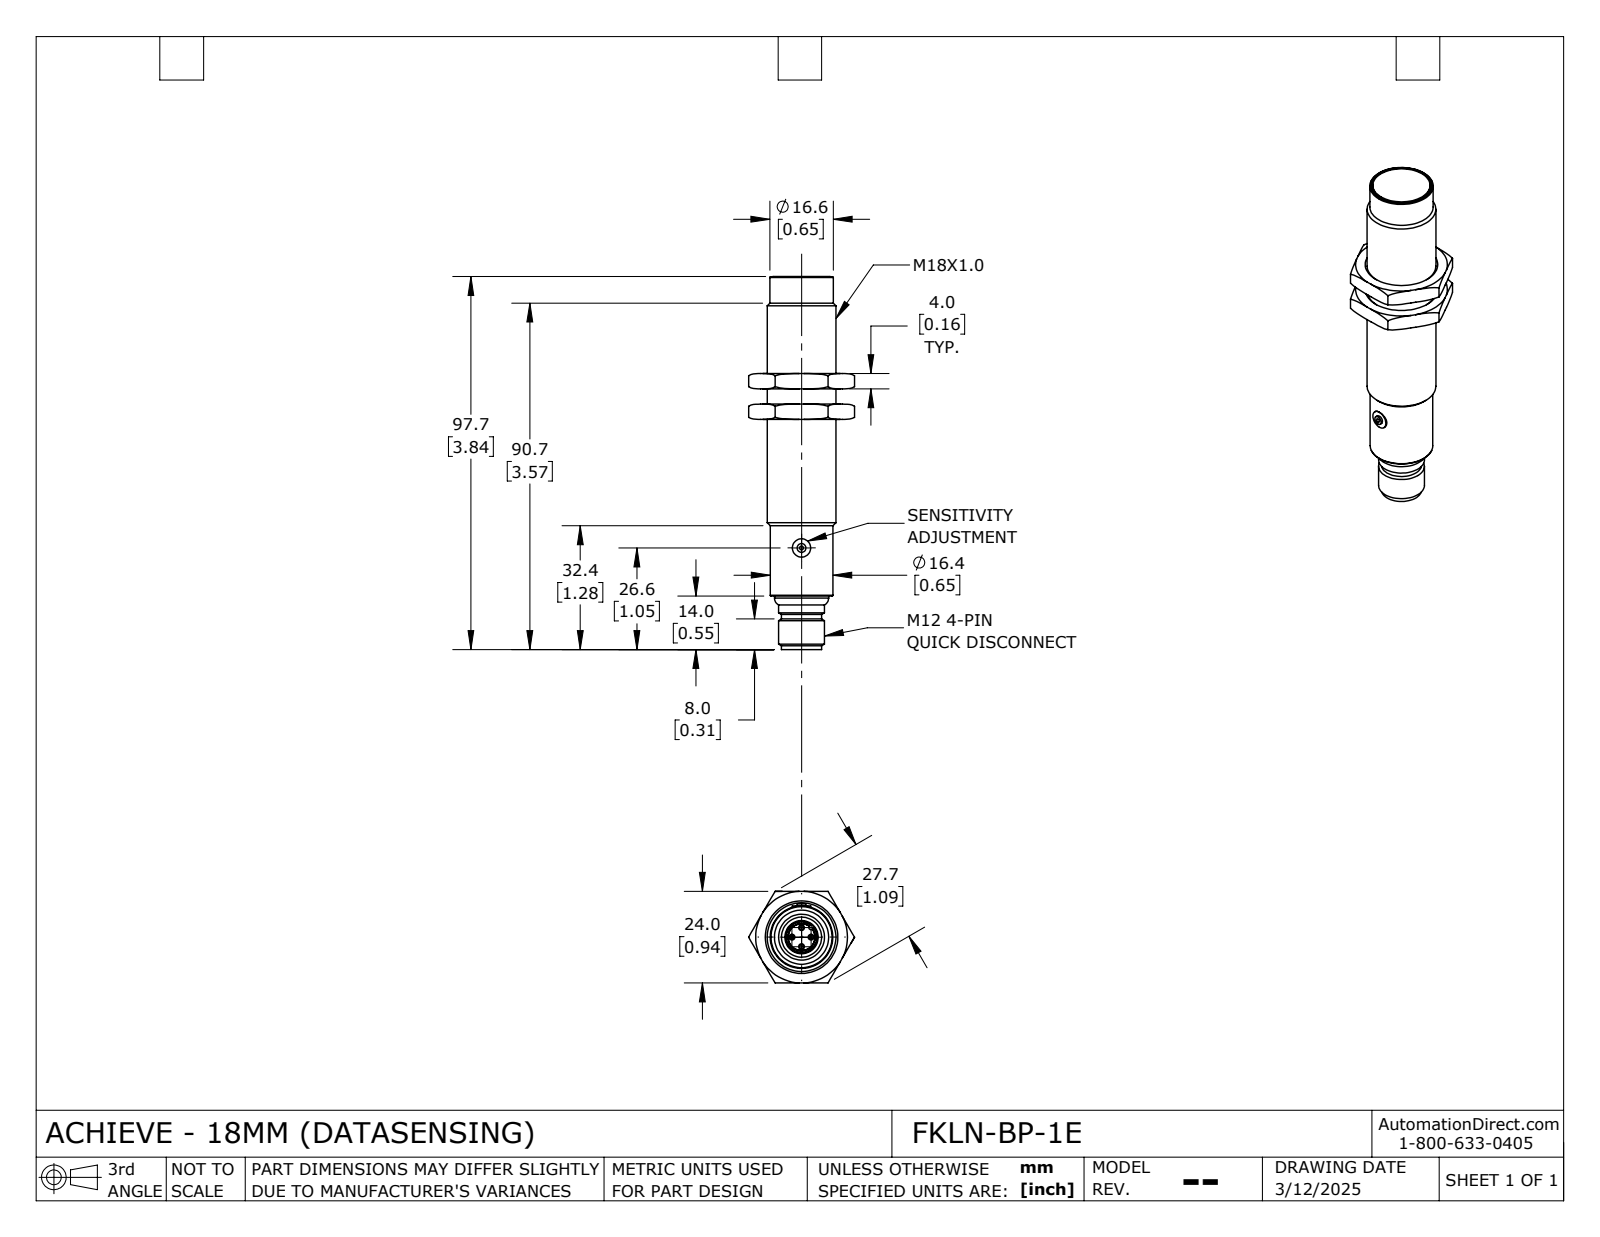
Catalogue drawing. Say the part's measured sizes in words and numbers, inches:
The part is named "FKLN-BP-1E_Default". Its 3-D file was written by "SolidWorks 2024 (CONFIG_CONTROL_DESIGN)". It is 3 solids with 121 faces: 43 planar, 29 cylindrical and 49 other. Overall it measures 3.844 by 1.091 by 0.945 inches. Its volume is 1.404 cubic inches and its surface area 14.06 square inches. Round holes: 1 of diameter 0.185, 1 of diameter 0.278, 1 of diameter 0.327, 1 of diameter 0.587, 1 of diameter 0.709. Round bosses or shafts: 4 of diameter 0.039, 1 of diameter 0.654, 1 of diameter 0.646, 1 of diameter 0.591, 1 of diameter 0.583, 1 of diameter 0.559, 1 of diameter 0.472, 1 of diameter 0.413. Partial cylindrical surfaces (rounded edges, fillets, slot ends): 2 of radius 0.02, 1 of radius 0.024, 1 of radius 0.297. The main face-to-face distances are 0.157, 0.315, 0.945, 0.093, 0.1, 1.215, 1.222, 1.315, 0.9, 0.907.
